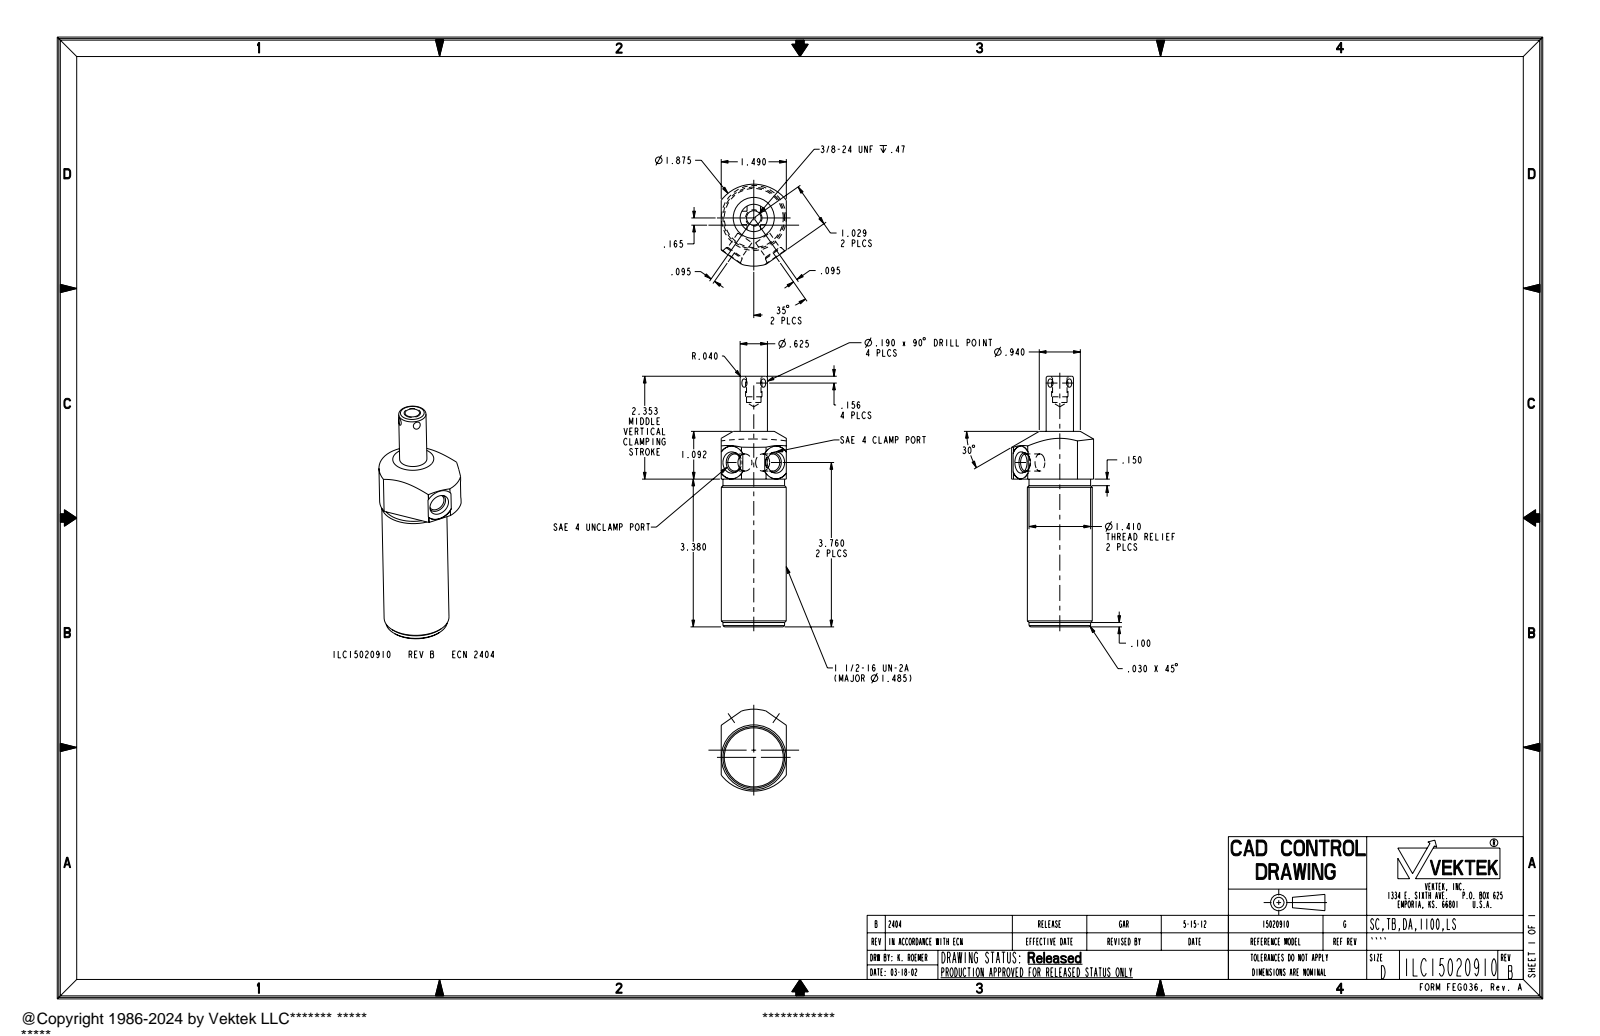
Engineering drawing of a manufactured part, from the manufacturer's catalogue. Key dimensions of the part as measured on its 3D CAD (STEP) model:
Part name (STEP PRODUCT): ILC15020910
STEP written by: PRO/ENGINEER BY PARAMETRIC TECHNOLOGY CORPORATION, 2007460 (AUTOMOTIVE_DESIGN_CC2)
Units: inches
Bodies: 1 solid, 69 faces (15 planar, 26 cylindrical, 28 other)
Overall size (bounding box): 5.733 × 1.875 × 1.49
Volume: 8.386 in³ · Surface area: 30.72 in²
Round holes (diameter × count): ⌀0.392 ×2, ⌀0.332 ×1
Round bosses / shafts (diameter × count): ⌀1.485 ×1, ⌀1.41 ×1, ⌀0.625 ×1, ⌀0.375 ×1
Partial cylindrical surfaces — rounded edges, fillets, slot ends (radius × count): R0.375 ×2, R0.937 ×1
Main face-to-face distances: 1.49, 3.38, 4.472, 1.092, 0.53, 5.733, 2.353, 1.261, 0.54, 0.54
